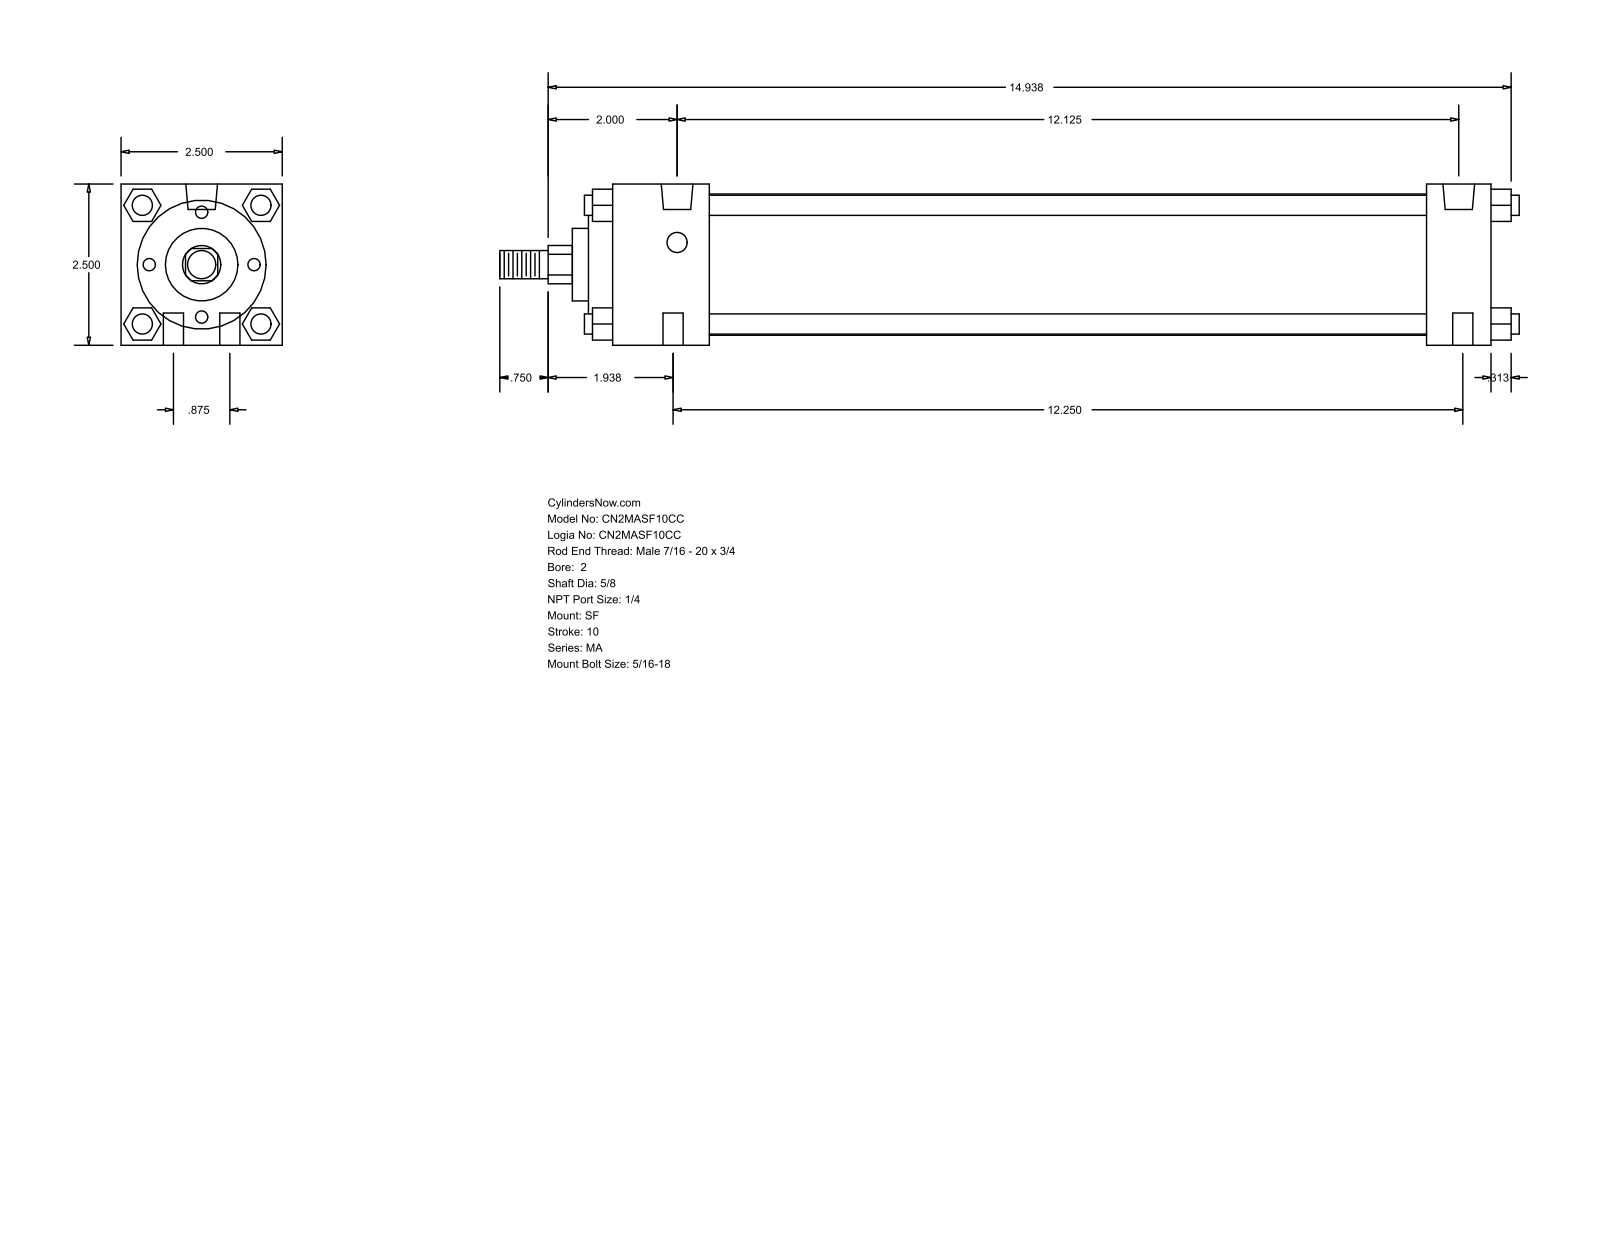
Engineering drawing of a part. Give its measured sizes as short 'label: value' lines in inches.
name: MA_SF__0200_0.625
written by: GSSL Pune (CONFIG_CONTROL_DESIGN)
unit: in
bodies: 0 solids, 126 faces (95 planar, 31 cylindrical, 0 other)
size: 15.813 × 2.5 × 2.5
holes: 6× ⌀0.313, 2× ⌀0.492
bosses: 4× ⌀0.313, 1× ⌀2.19, 1× ⌀2, 1× ⌀1.125, 1× ⌀0.625, 1× ⌀0.437
rounds: 1× R0.297
face distances: 2.5, 0.5, 1.5, 13.625, 12.625, 1, 11.125, 12.125, 0.375, 1.875
hole spacings: 0.442, 12.195, 0.875, 12.125, 12.25, 12.281
